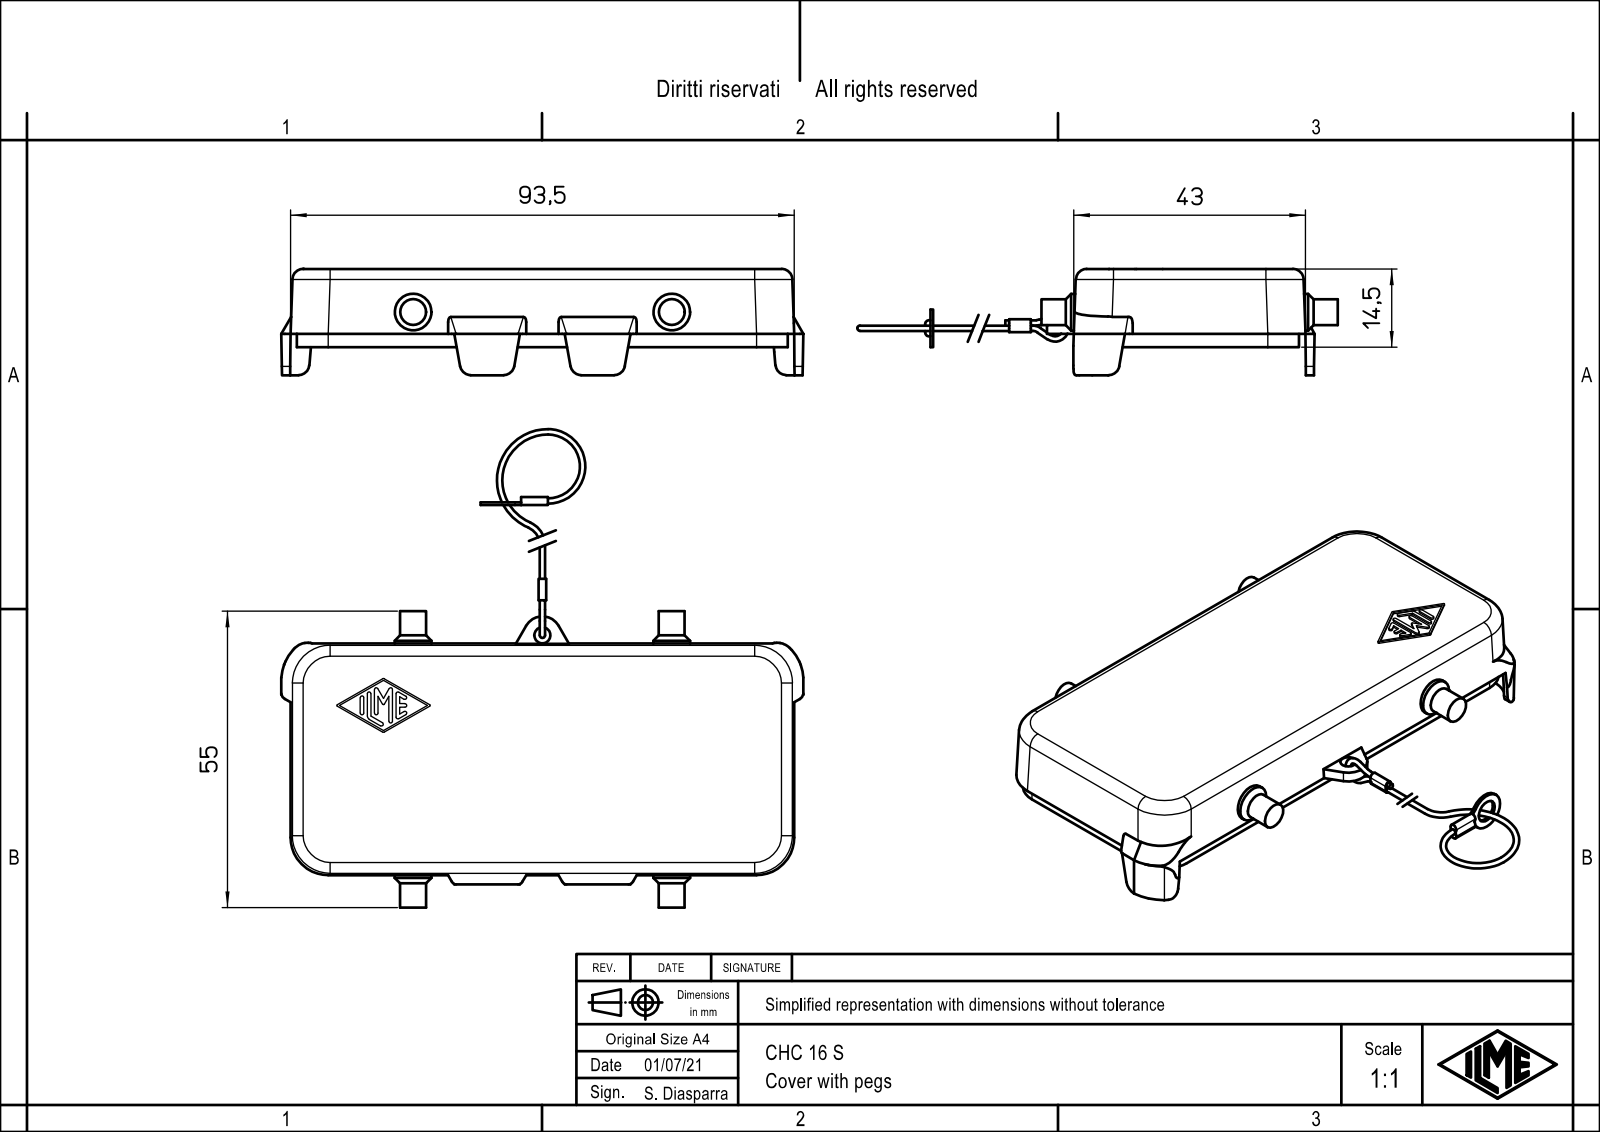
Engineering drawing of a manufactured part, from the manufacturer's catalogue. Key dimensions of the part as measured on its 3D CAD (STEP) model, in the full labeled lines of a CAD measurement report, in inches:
Part name (STEP PRODUCT): CHC_16_S
STEP written by: Creo Elements/Direct Modeling 20.1B 02-Apr-2019 (C) Parametric Technology GmbH (AUTOMOTIVE_DESIGN)
Units: inches
Bodies: 1 solid, 248 faces (75 planar, 95 cylindrical, 78 other)
Overall size (bounding box): 8.83 × 3.815 × 0.776
Volume: 1.317 in³ · Surface area: 25.61 in²
Round holes (diameter × count): ⌀0.118 ×1, ⌀0.165 ×1
Round bosses / shafts (diameter × count): ⌀0.039 ×4, ⌀0.268 ×2, ⌀0.189 ×2, ⌀0.039 ×2, ⌀0.276 ×1
Partial cylindrical surfaces — rounded edges, fillets, slot ends (radius × count): R0.018 ×18, R0.079 ×11, R0.031 ×4, R0.049 ×4, R0.165 ×4, R0.228 ×4, R0.276 ×4, R0.028 ×2
Main face-to-face distances: 0.098, 0.472, 0.374, 0.063, 1.535, 0.571, 1.598, 1.472, 3.524, 3.587
